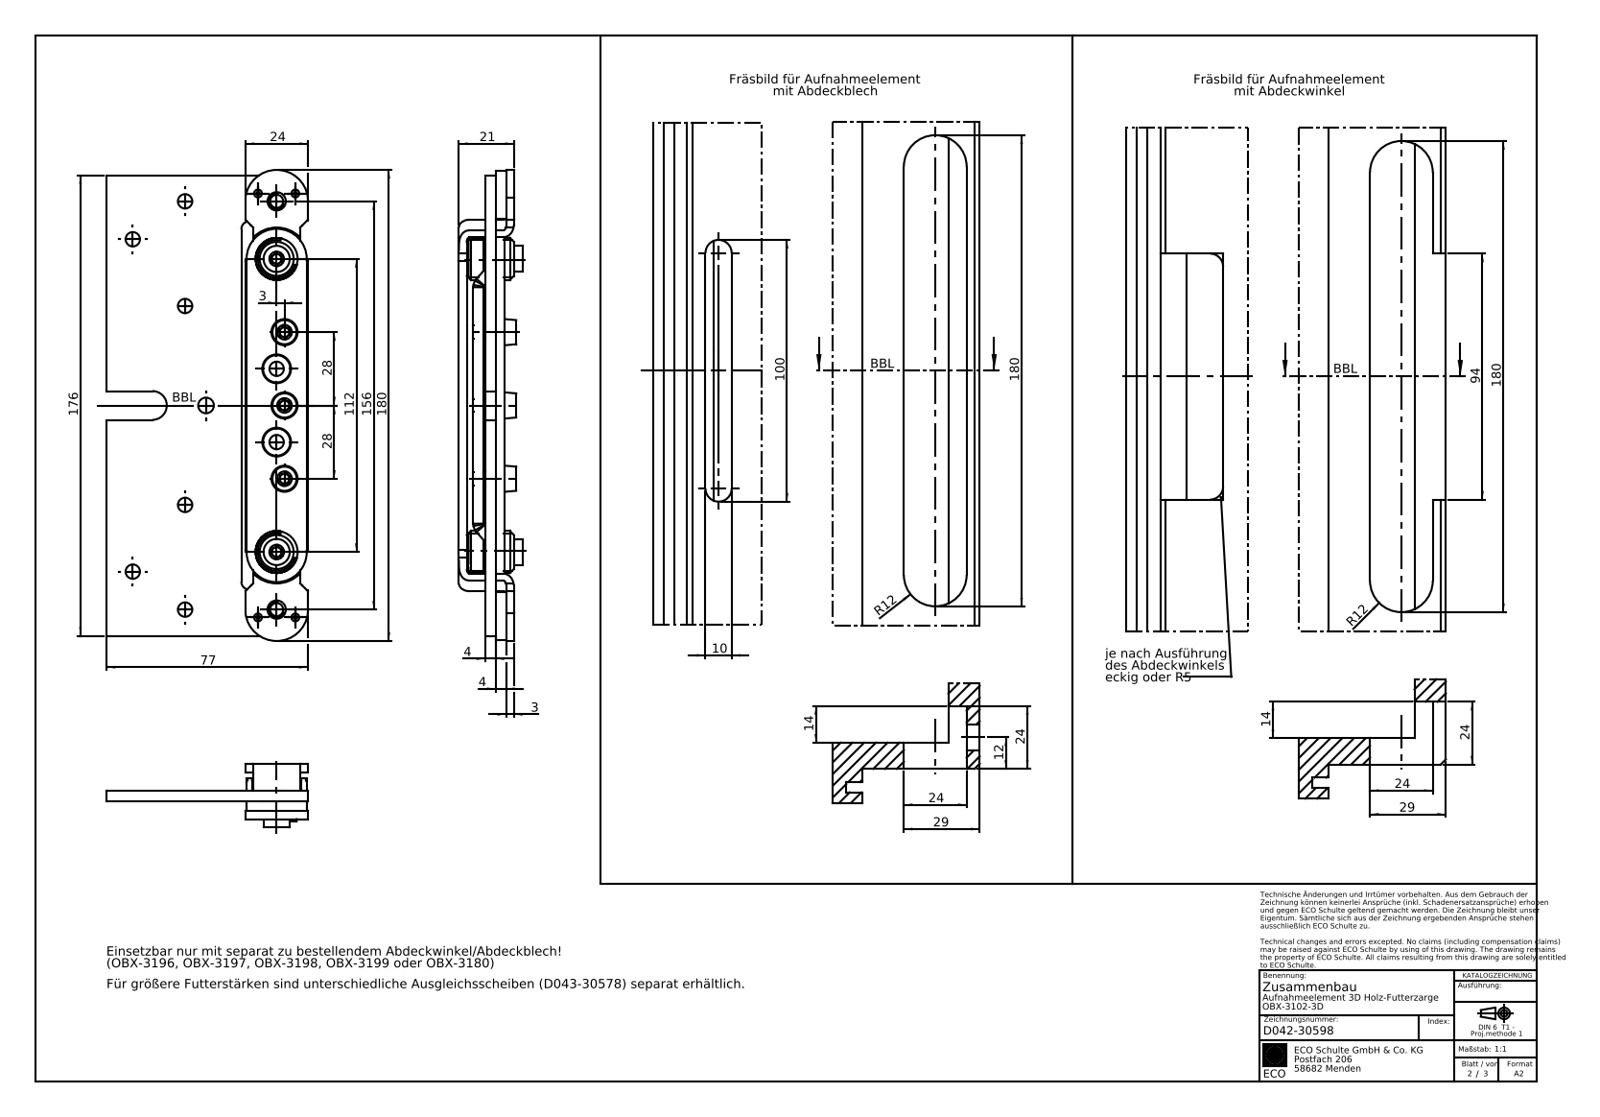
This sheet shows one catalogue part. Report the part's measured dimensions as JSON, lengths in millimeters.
{"part_name": "D042-28530_3mm-Mitte-Band; D043-30794_Futterzarge; D047-28560_ISO 14580 - #6 x 12 x 10 - 4.8-C; B01456 (+7 more)", "step_written_by": "SolidWorks 2020 (AUTOMOTIVE_DESIGN)", "units": "millimeters", "bodies": {"solids": 11, "faces": 471, "planar": 188, "cylindrical": 157, "other": 126}, "overall_size": [180, 77, 24.25], "volume_mm3": 78977, "surface_area_mm2": 51327, "round_holes": [[5.5, 8], [5, 5], [5.6, 5], [11, 4], [6.5, 3], [7, 2], [8.2, 2], [14.5, 2], [6, 1]], "round_bosses_or_shafts": [[6, 3], [19, 2], [16, 2], [10, 2], [8.6, 2], [8, 2]], "partial_cylinders_radius": [[1, 10], [3, 6], [11.5, 4], [12, 4], [3.25, 3], [2, 2], [4.5, 2], [5, 2]], "face_to_face_distances": [4, 0.5, 4.5, 3.5, 8, 11, 3, 7, 8.5, 7.5], "hole_center_spacings": [14.32, 28, 22, 24.7, 28.16, 30.41, 32.41, 35]}
